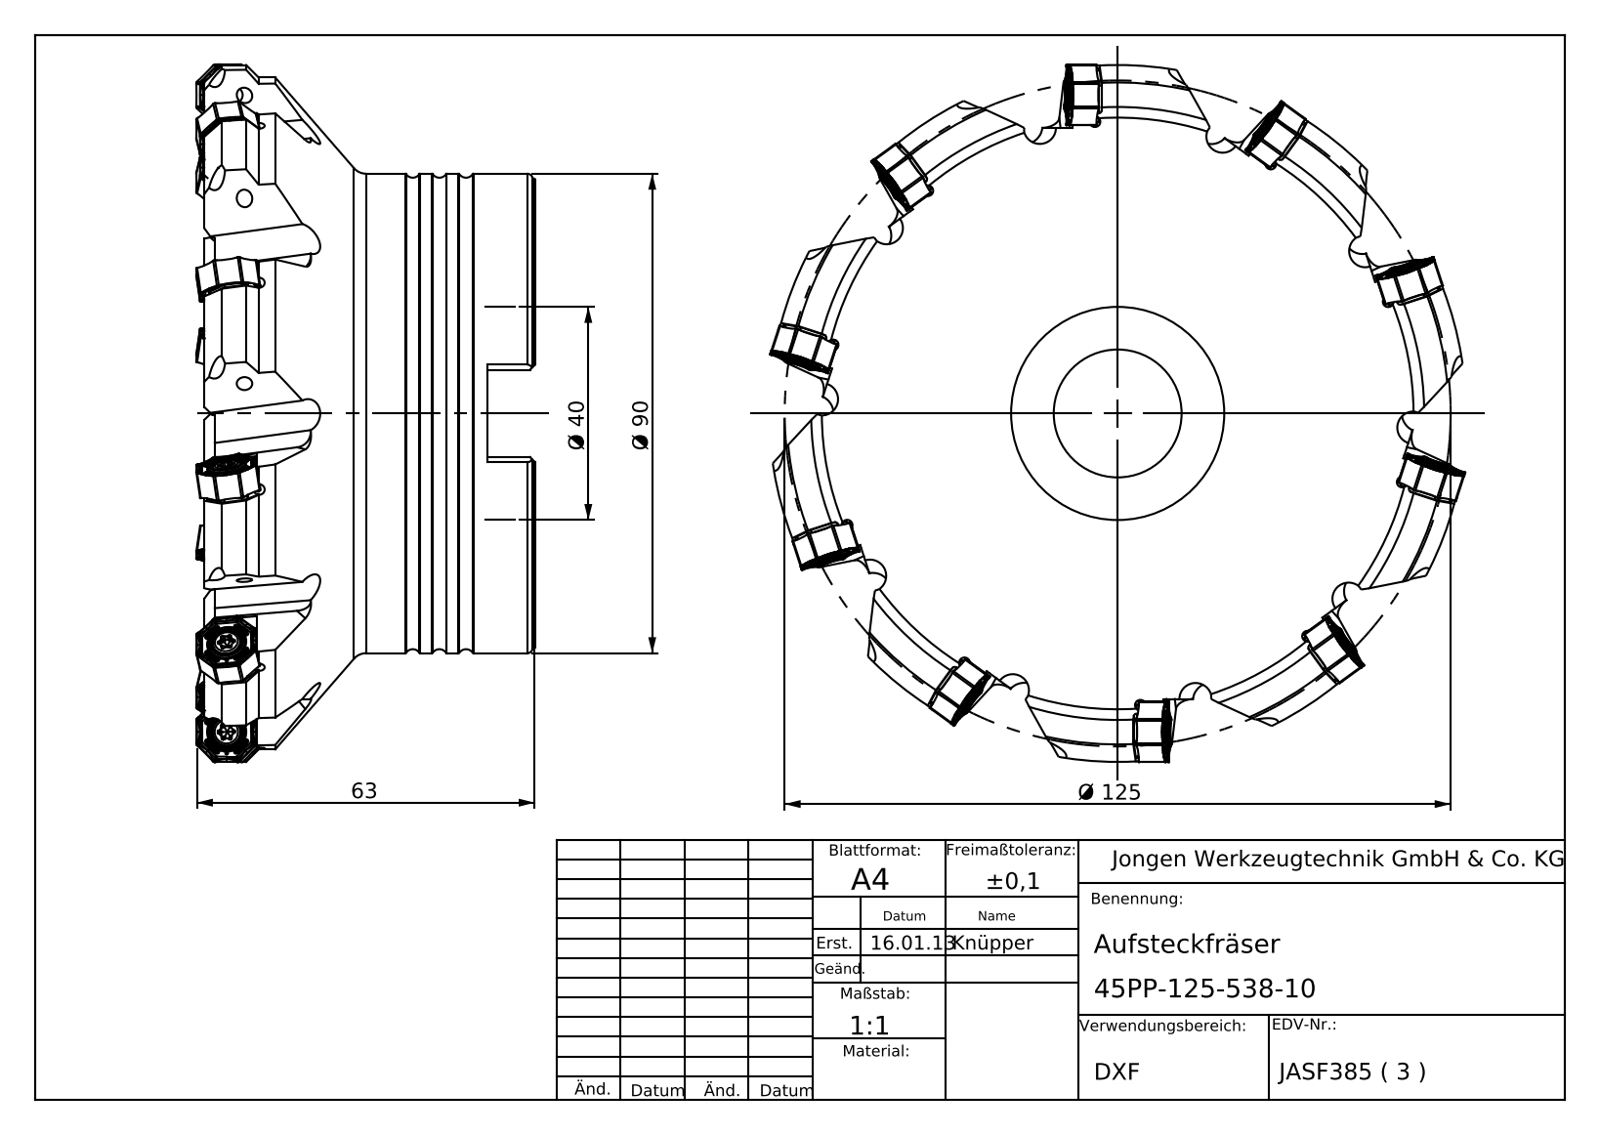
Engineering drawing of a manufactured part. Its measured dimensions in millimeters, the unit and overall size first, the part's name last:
Units: millimetres
Overall size (bounding box): 132.16 × 132.16 × 63.08
Round holes (diameter × count): ⌀3 ×10, ⌀24 ×1, ⌀40 ×1, ⌀40.15 ×1, ⌀40.3 ×1
Round bosses / shafts (diameter × count): ⌀90 ×1
Partial cylindrical surfaces — rounded edges, fillets, slot ends (radius × count): R1 ×20, R1.25 ×10, R3 ×10, R63.05 ×1, R65.4 ×1
Main face-to-face distances: 60.1, 8.95, 51.15, 27.95, 19, 32.15, 16.4, 107.18, 0.47, 45.39
Volume: 440 761 mm³ · Surface area: 56 262 mm²
Bodies: 1 solid, 475 faces (162 planar, 160 cylindrical, 153 other)
Part name (STEP PRODUCT): 45PP-125-538-10
STEP written by: SolidWorks 2013 (AUTOMOTIVE_DESIGN)
